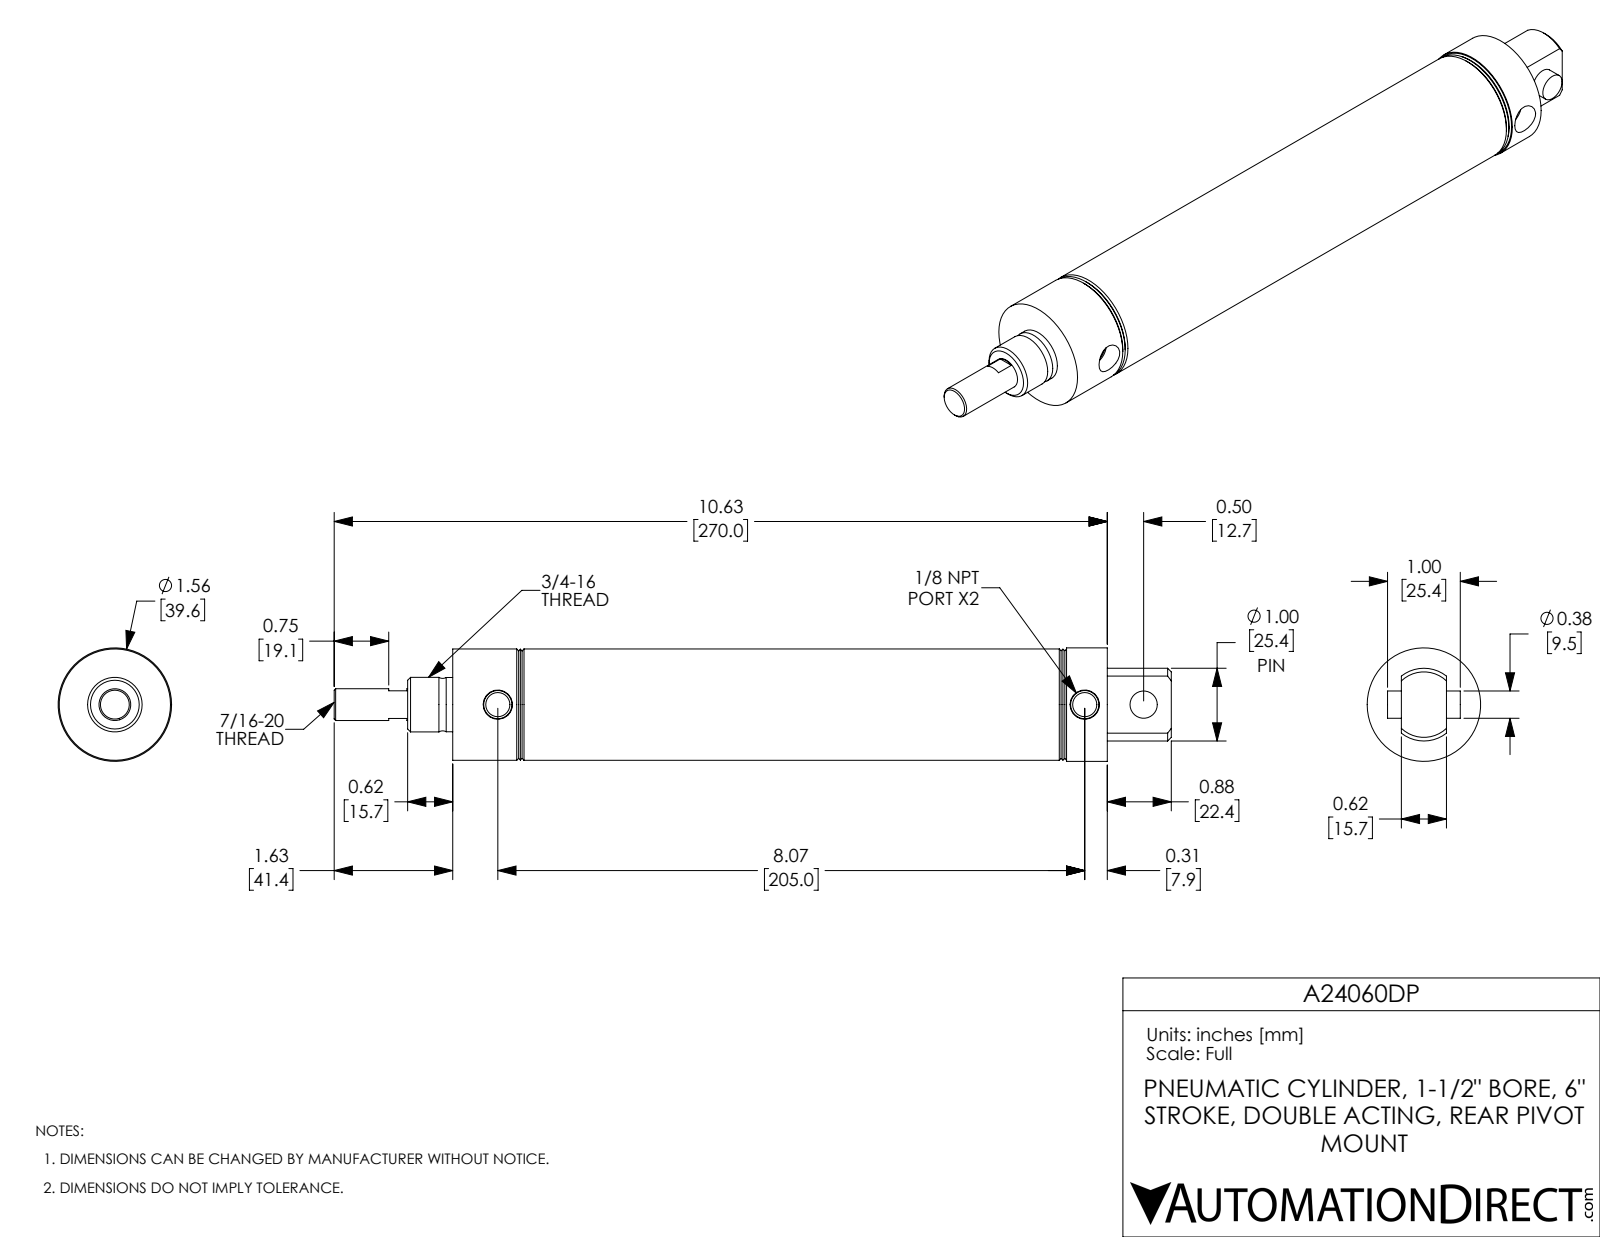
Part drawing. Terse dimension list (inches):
name: A24060DP-Pin; A24060DP; A24060DP-MainBody; A24060DP-Rod
written by: SolidWorks 2017 (AUTOMOTIVE_DESIGN)
unit: in
bodies: 3 solids, 84 faces (22 planar, 28 cylindrical, 34 other)
size: 11.51 × 1.56 × 1.56
volume: 7.737 in³; area: 108.8 in²
holes: 2× ⌀0.332, 1× ⌀0.375, 1× ⌀0.437, 1× ⌀1.5
bosses: 1× ⌀1.56, 1× ⌀1.53, 1× ⌀0.75, 1× ⌀0.746
rounds: 1× R0.5
face distances: 1.25, 7.75, 6.5, 0.5, 6, 7.25, 1.75, 9, 0.62, 0.88
hole spacings: 0.81, 8.07, 8.88
